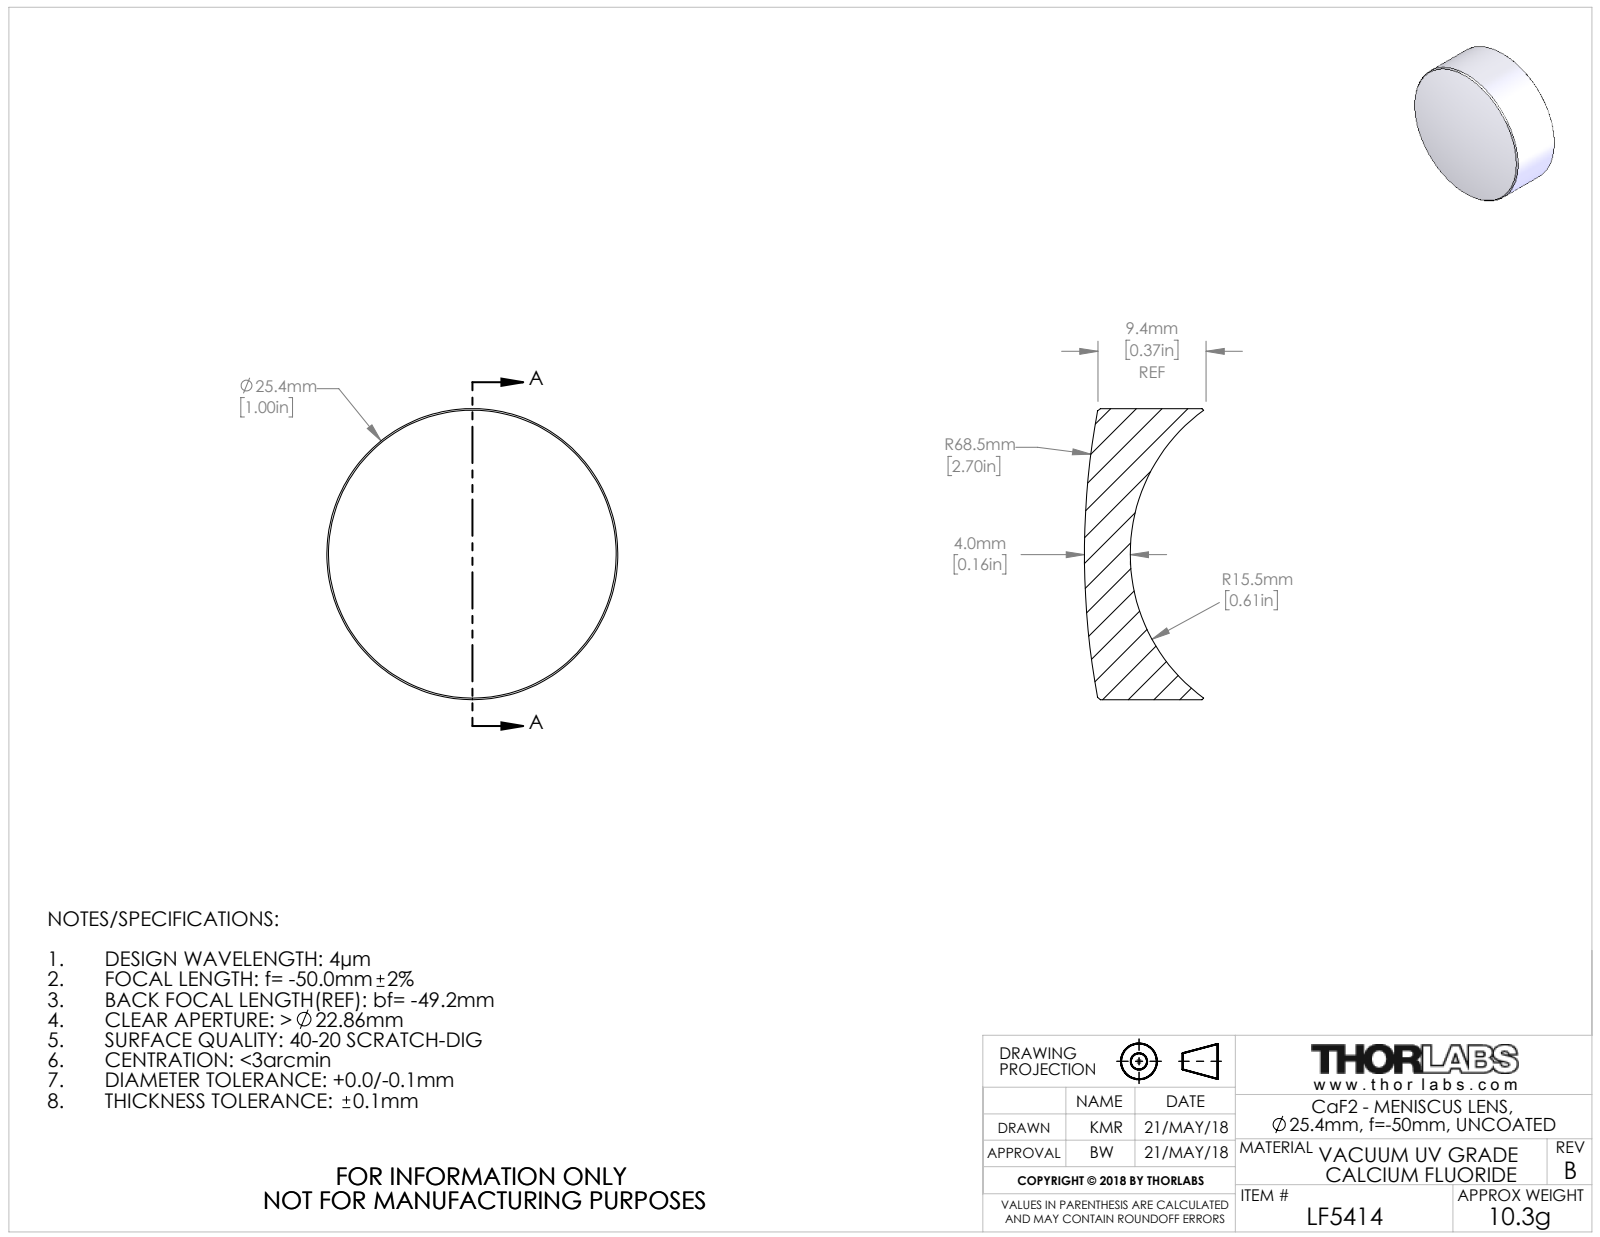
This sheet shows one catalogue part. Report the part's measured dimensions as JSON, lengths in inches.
{"part_name": "21999-E0W", "step_written_by": "SolidWorks 2016 (CONFIG_CONTROL_DESIGN)", "units": "inches", "bodies": {"solids": 1, "faces": 10, "planar": 0, "cylindrical": 2, "other": 8}, "overall_size": [1, 1, 0.41], "volume_in3": 0.198, "surface_area_in2": 2.898, "round_bosses_or_shafts": [[1, 1]]}
